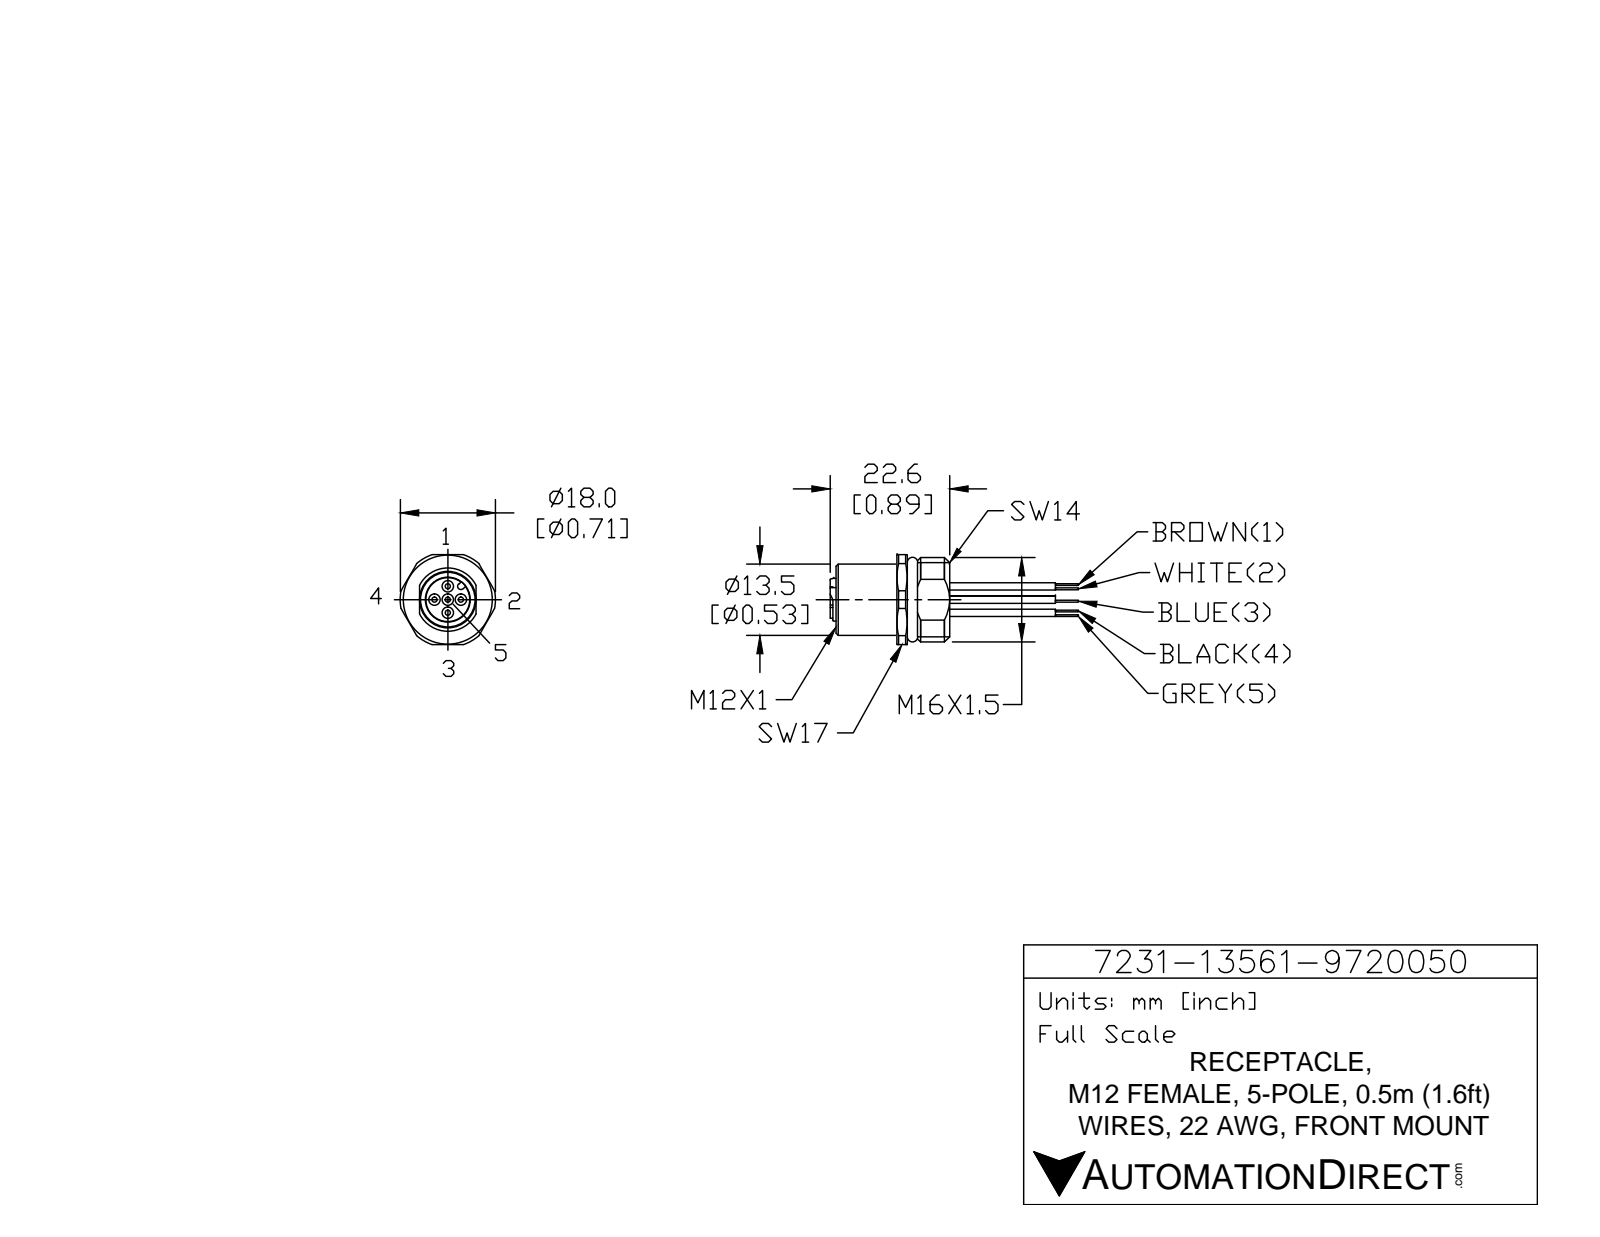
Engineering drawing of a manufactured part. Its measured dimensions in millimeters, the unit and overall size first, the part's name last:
Units: millimetres
Overall size (bounding box): 42.6 × 18 × 17
Round holes (diameter × count): ⌀1.1 ×5, ⌀10.92 ×1, ⌀12.2 ×1, ⌀13 ×1
Round bosses / shafts (diameter × count): ⌀2 ×5, ⌀1.4 ×5, ⌀13.5 ×1, ⌀8.1 ×1
Partial cylindrical surfaces — rounded edges, fillets, slot ends (radius × count): R0.2 ×6, R0.6 ×1, R8 ×1, R9 ×1
Main face-to-face distances: 7, 14.1, 9, 2, 7.1, 5.1, 14, 21.1, 1, 17
Hole centre spacings: 2.5, 3.54, 5, 2.49, 2.51
Volume: 3 370 mm³ · Surface area: 2 560 mm²
Bodies: 1 solid, 156 faces (39 planar, 65 cylindrical, 52 other)
Part name (STEP PRODUCT): 7231-13561-9720050
STEP written by: SolidWorks 2015 (AUTOMOTIVE_DESIGN)
